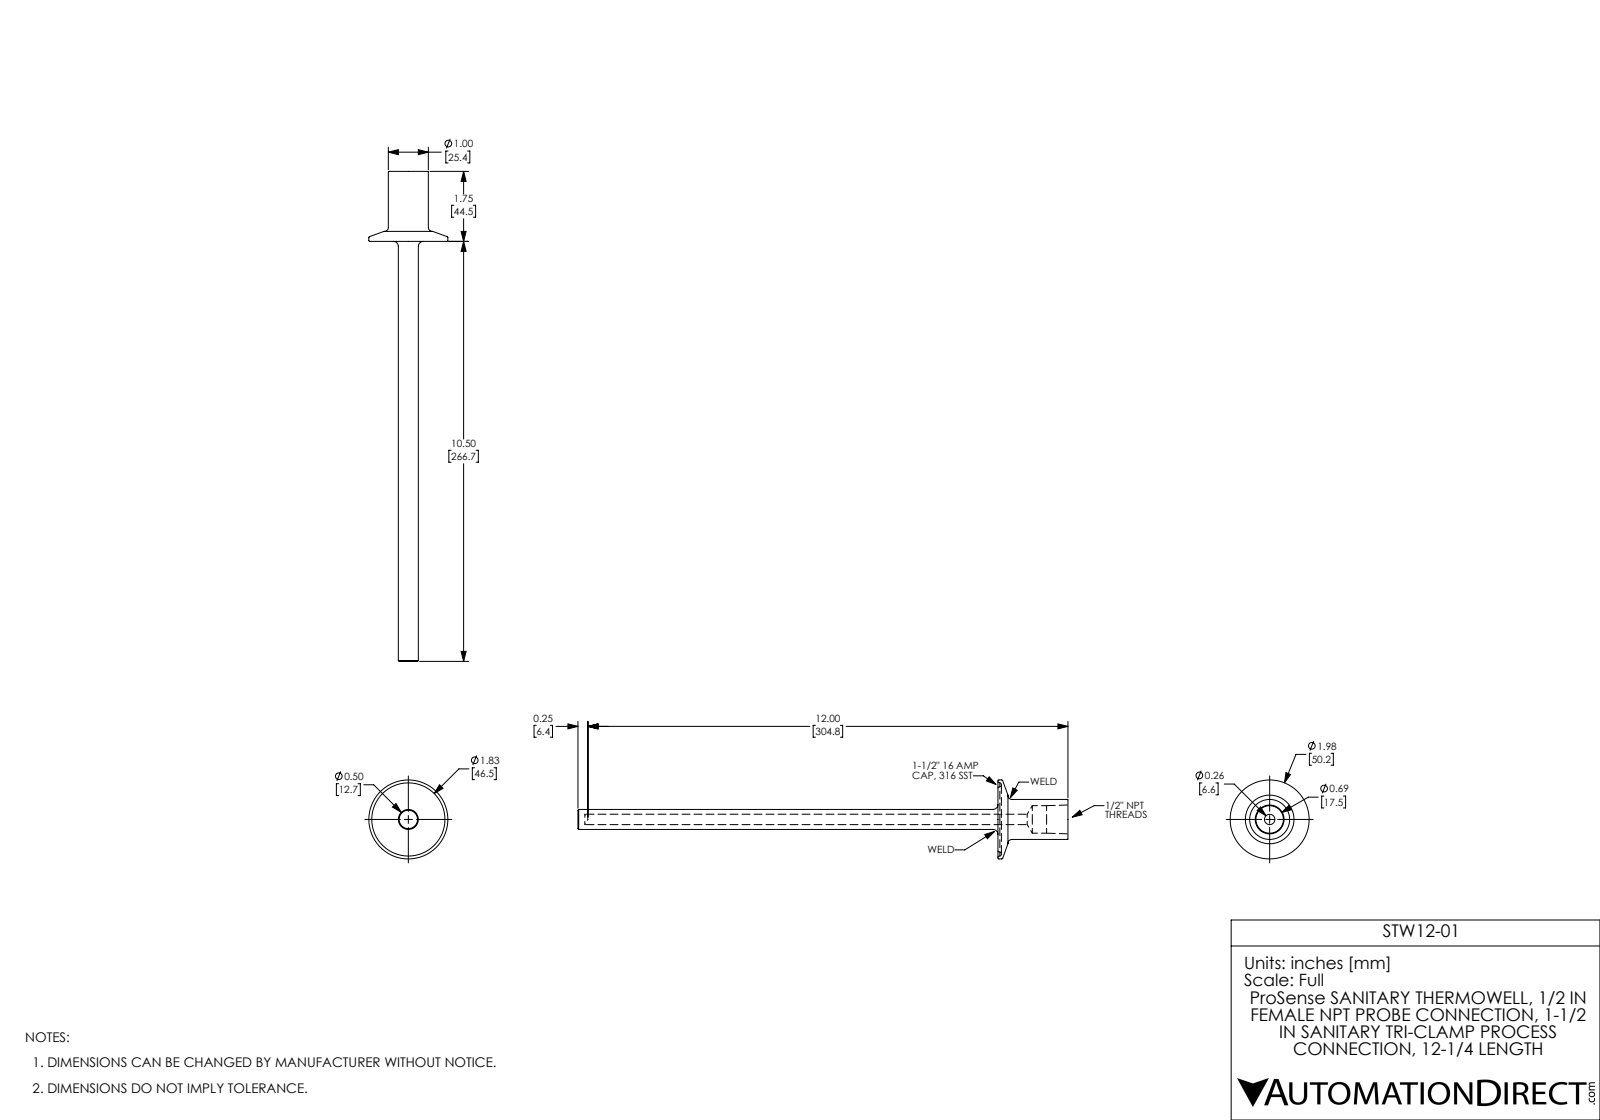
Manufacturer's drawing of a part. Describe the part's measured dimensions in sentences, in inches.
The part is named "STW12-01". Its 3-D file was written by "SolidWorks 2017 (AUTOMOTIVE_DESIGN)". It is 1 solid with 45 faces: 5 planar, 10 cylindrical and 30 other. Overall it measures 12.25 by 1.975 by 1.975 inches. Its volume is 2.881 cubic inches and its surface area 39.36 square inches. Round holes: 1 of diameter 0.26, 1 of diameter 0.688. Round bosses or shafts: 1 of diameter 1.975, 1 of diameter 1, 1 of diameter 0.5. The main face-to-face distances are 1.75, 12.25, 10.5, 1.5, 0.25, 10.75.
